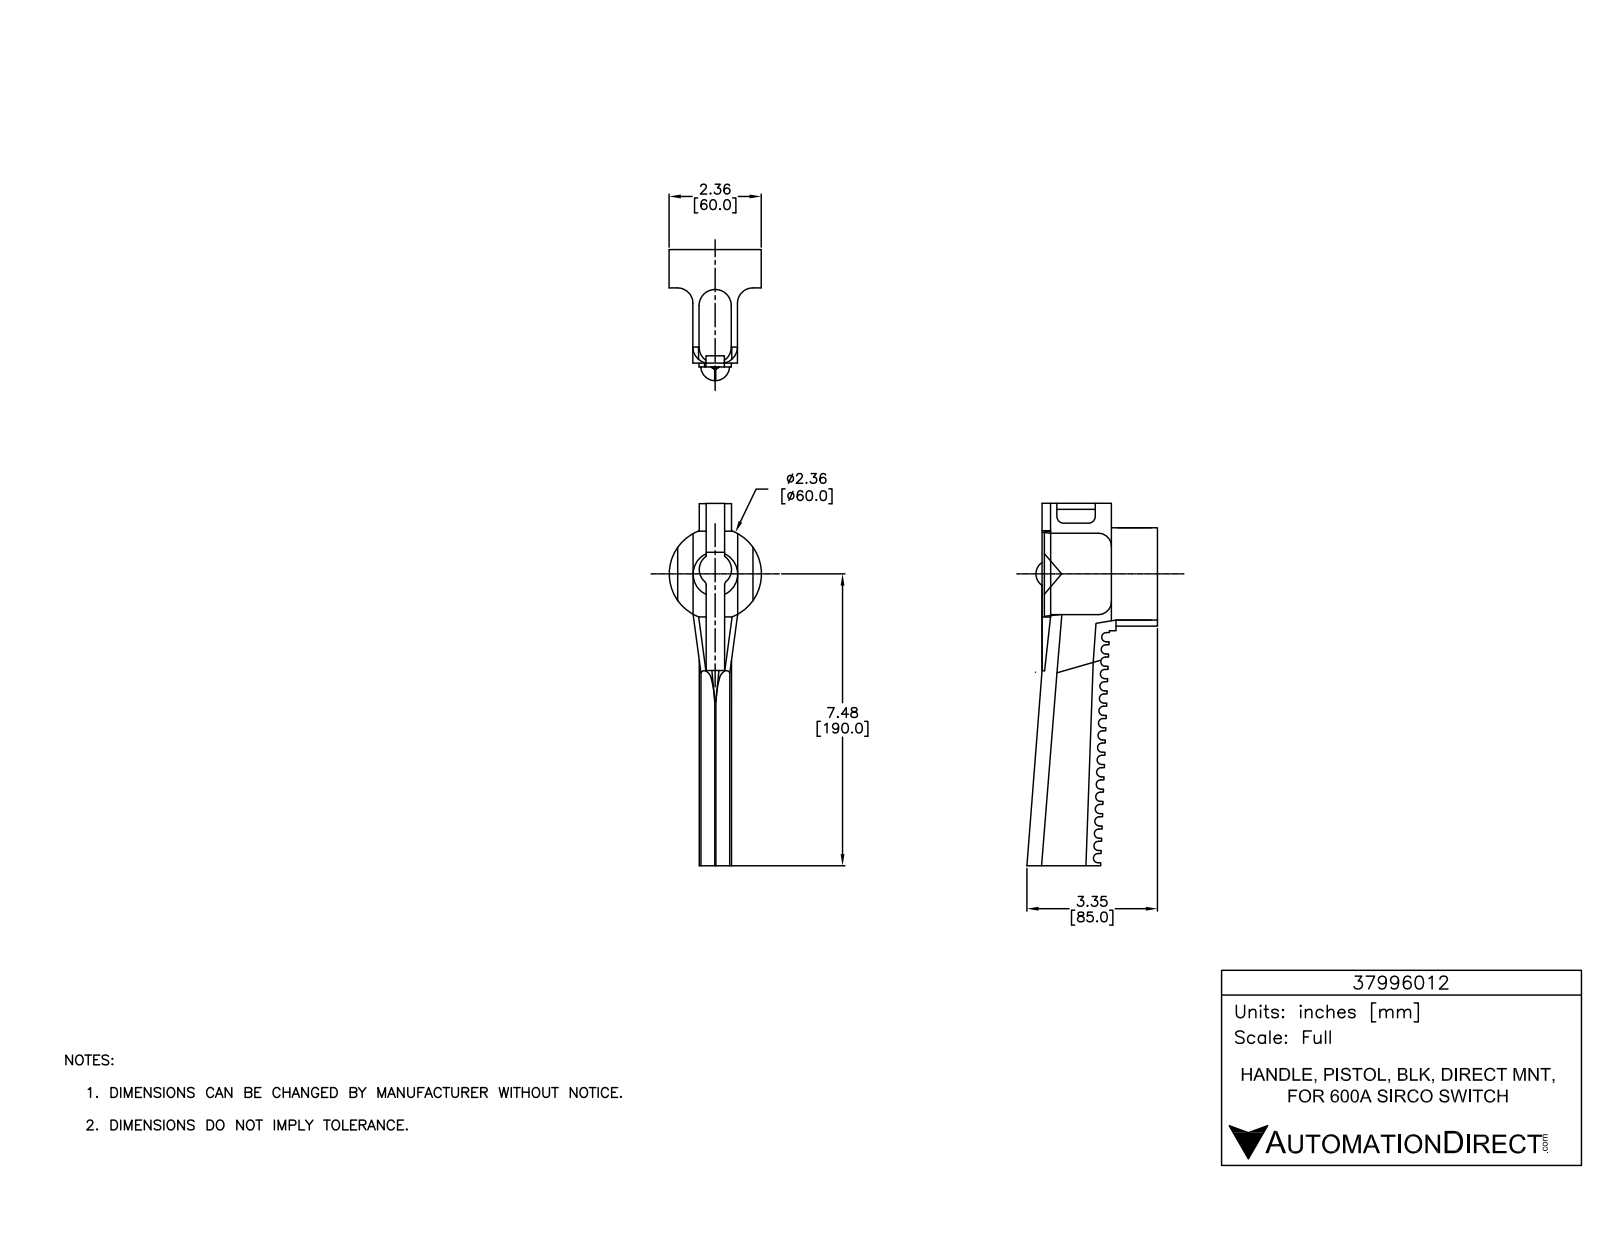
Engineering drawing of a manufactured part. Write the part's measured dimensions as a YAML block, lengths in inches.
part_name: "37996012"
step_written_by: "SolidWorks 2015 (AUTOMOTIVE_DESIGN)"
units: inches
bodies: {solids: 1, faces: 144, planar: 71, cylindrical: 68, other: 5}
overall_size: [9.286, 3.362, 2.362]
volume: 18.63
surface_area: 71.87
round_bosses_or_shafts:
  - {diameter: 2.362, count: 1}
partial_cylinders:
  - {radius: 0.118, count: 21}
  - {radius: 0.413, count: 5}
  - {radius: 0.354, count: 2}
  - {radius: 0.394, count: 2}
  - {radius: 0.114, count: 1}
  - {radius: 0.571, count: 1}
  - {radius: 1.181, count: 1}
  - {radius: 1.189, count: 1}
face_to_face_distances: [1.142, 0.807, 0.984, 0.157, 0.335, 0.472, 3.008, 0.177, 0.65, 9.281]
